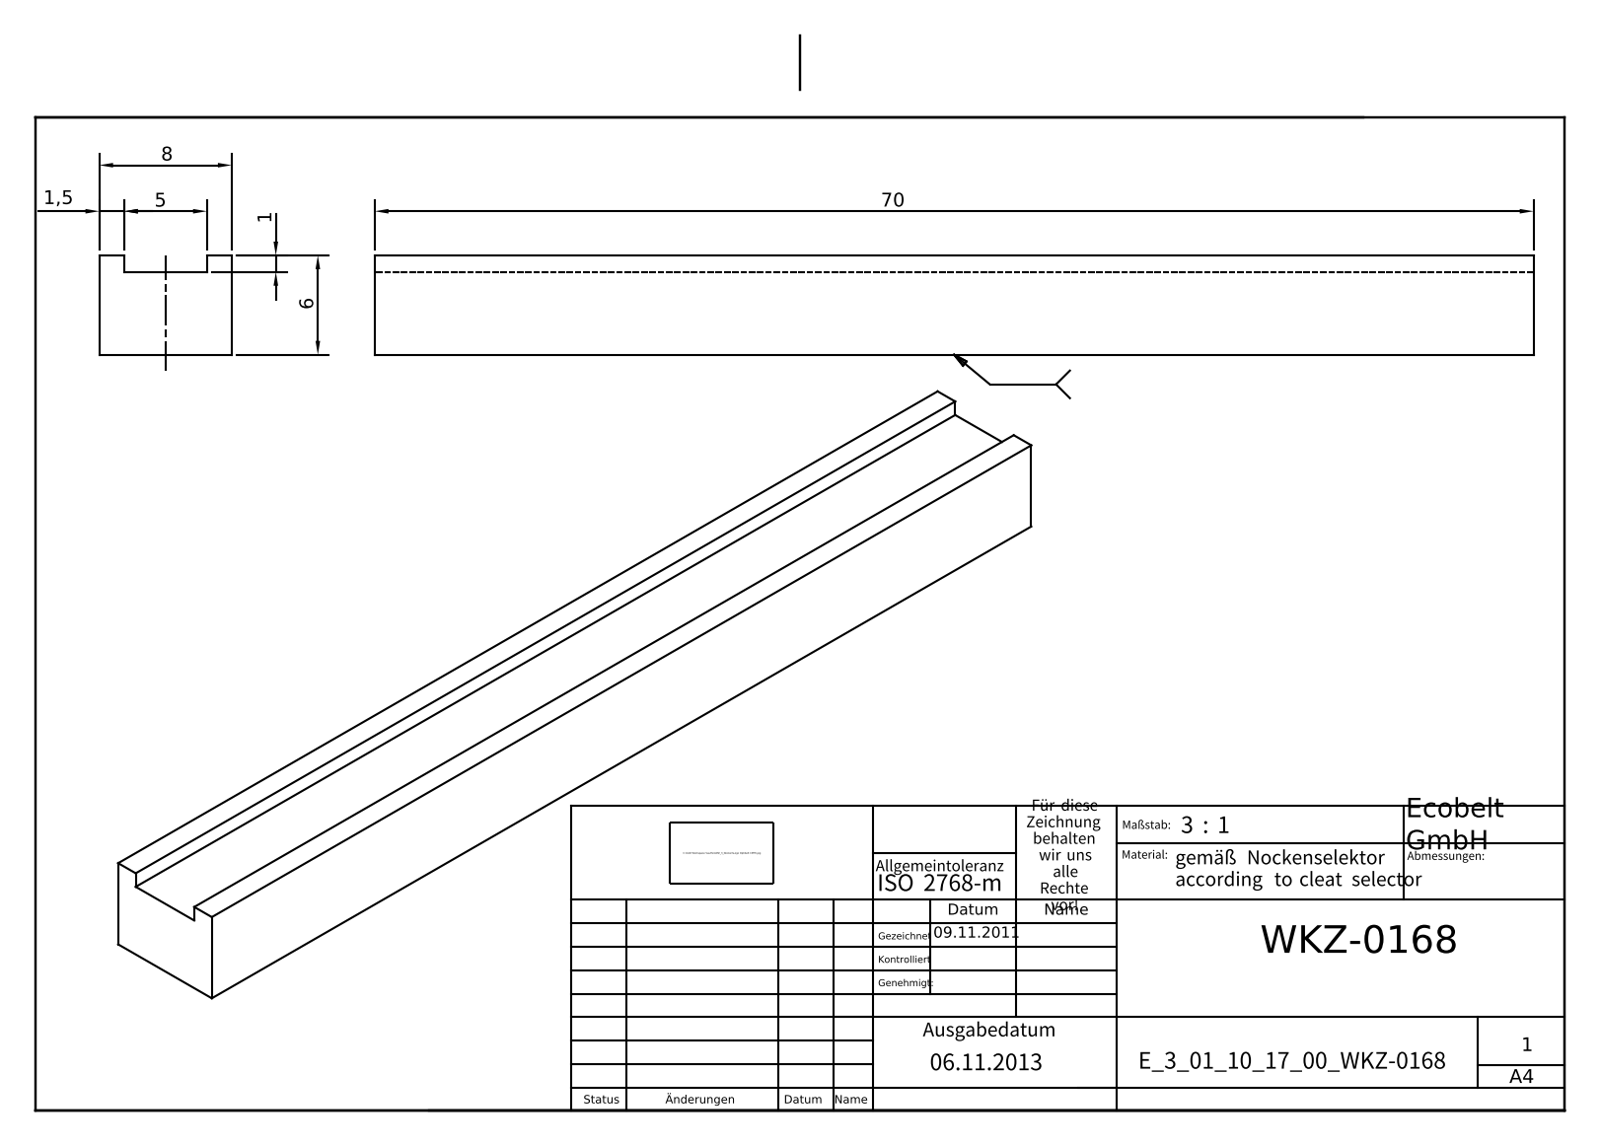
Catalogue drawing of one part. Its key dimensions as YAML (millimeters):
part_name: "E_3_01_10_17_00_WKZ-0168"
step_written_by: "Autodesk Inventor 2025 (AUTOMOTIVE_DESIGN)"
units: millimeters
bodies: {solids: 1, faces: 10, planar: 10, cylindrical: 0, other: 0}
overall_size: [70, 8, 6]
volume: 3010
surface_area: 2186
face_to_face_distances: [8, 5, 6, 1, 1.5, 6.5, 70]
